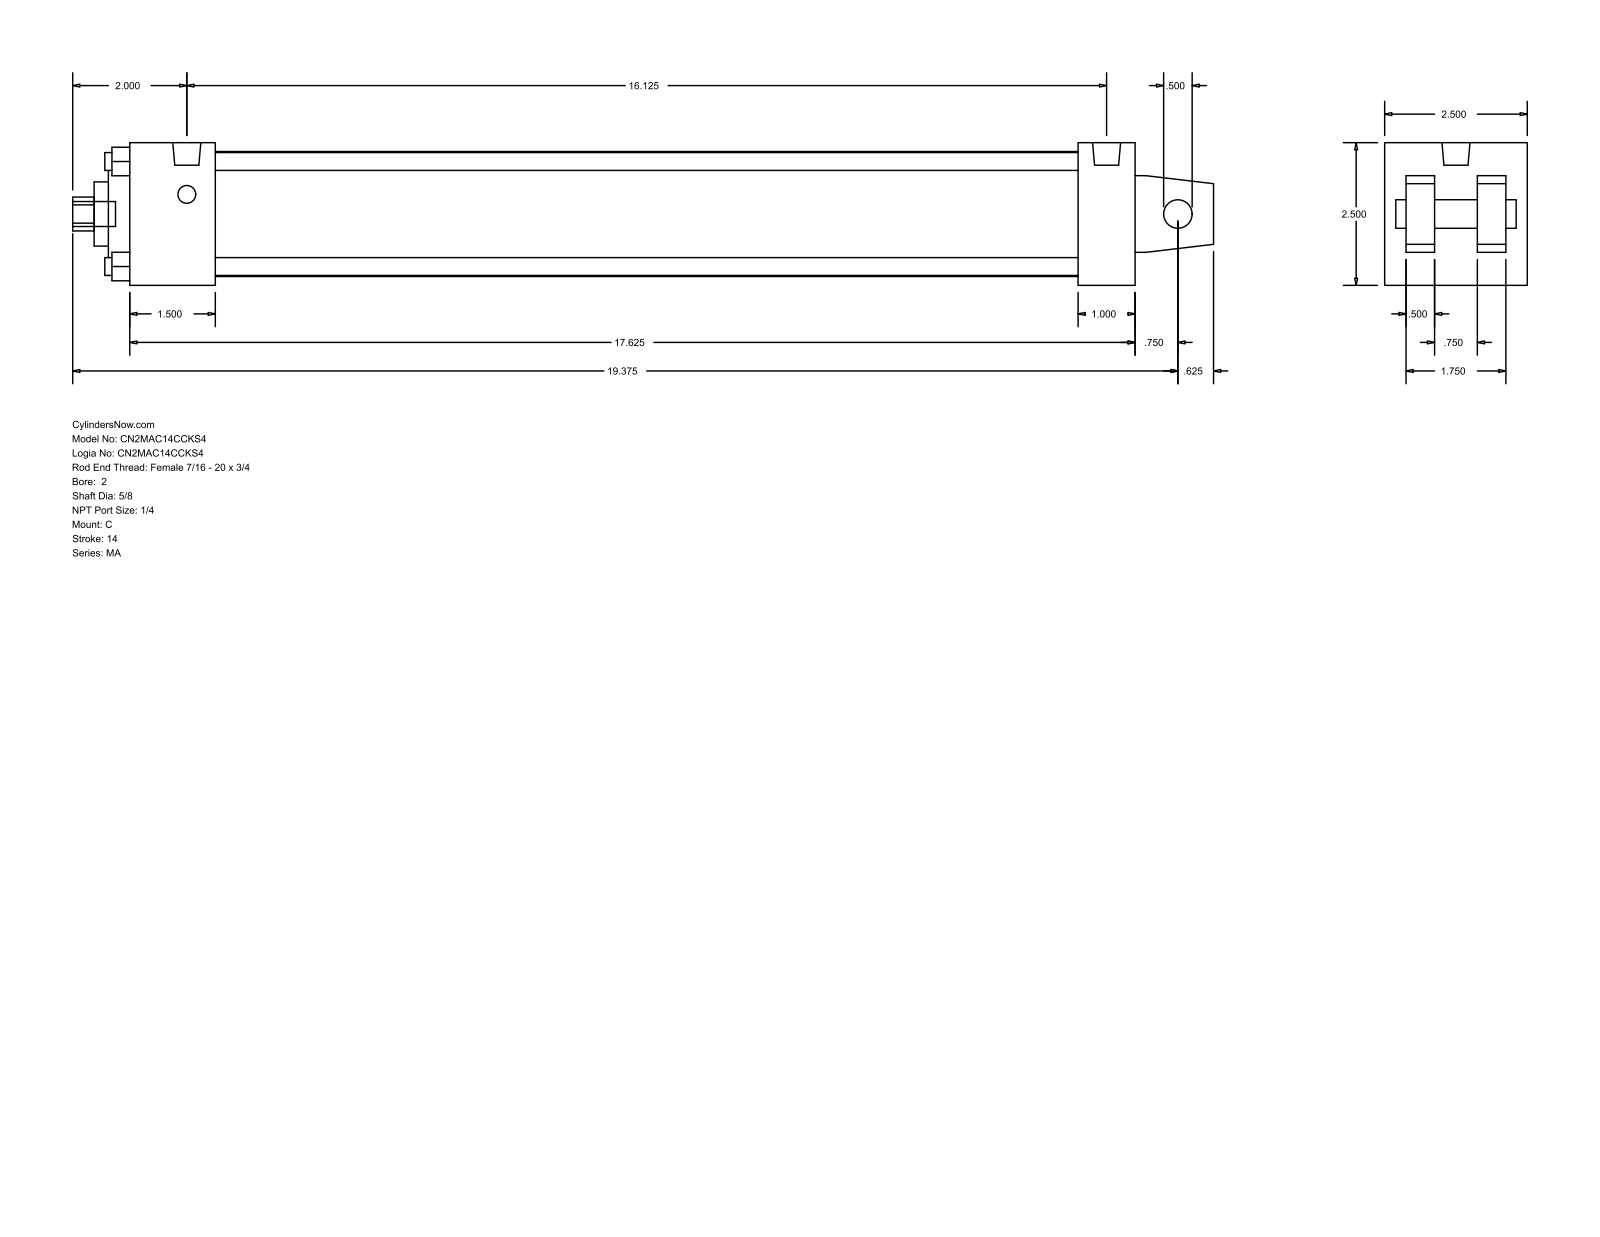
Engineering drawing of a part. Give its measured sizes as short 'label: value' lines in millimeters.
name: MA_C__0200_0.625
written by: GSSL Pune (CONFIG_CONTROL_DESIGN)
unit: mm
bodies: 0 solids, 105 faces (77 planar, 28 cylindrical, 0 other)
size: 508 × 63.5 × 63.5
holes: 4× ⌀7.94, 1× ⌀12.7, 1× ⌀15.88, 1× ⌀28.57, 1× ⌀50.8, 1× ⌀55.63
bosses: 4× ⌀7.94, 2× ⌀12.49, 1× ⌀11.11
rounds: 1× R7.54
face distances: 63.5, 9.52, 12.7, 22.22, 41.28, 53.98, 31.76, 38.1, 447.67, 409.57
hole spacings: 33.05, 46.74, 66.1
